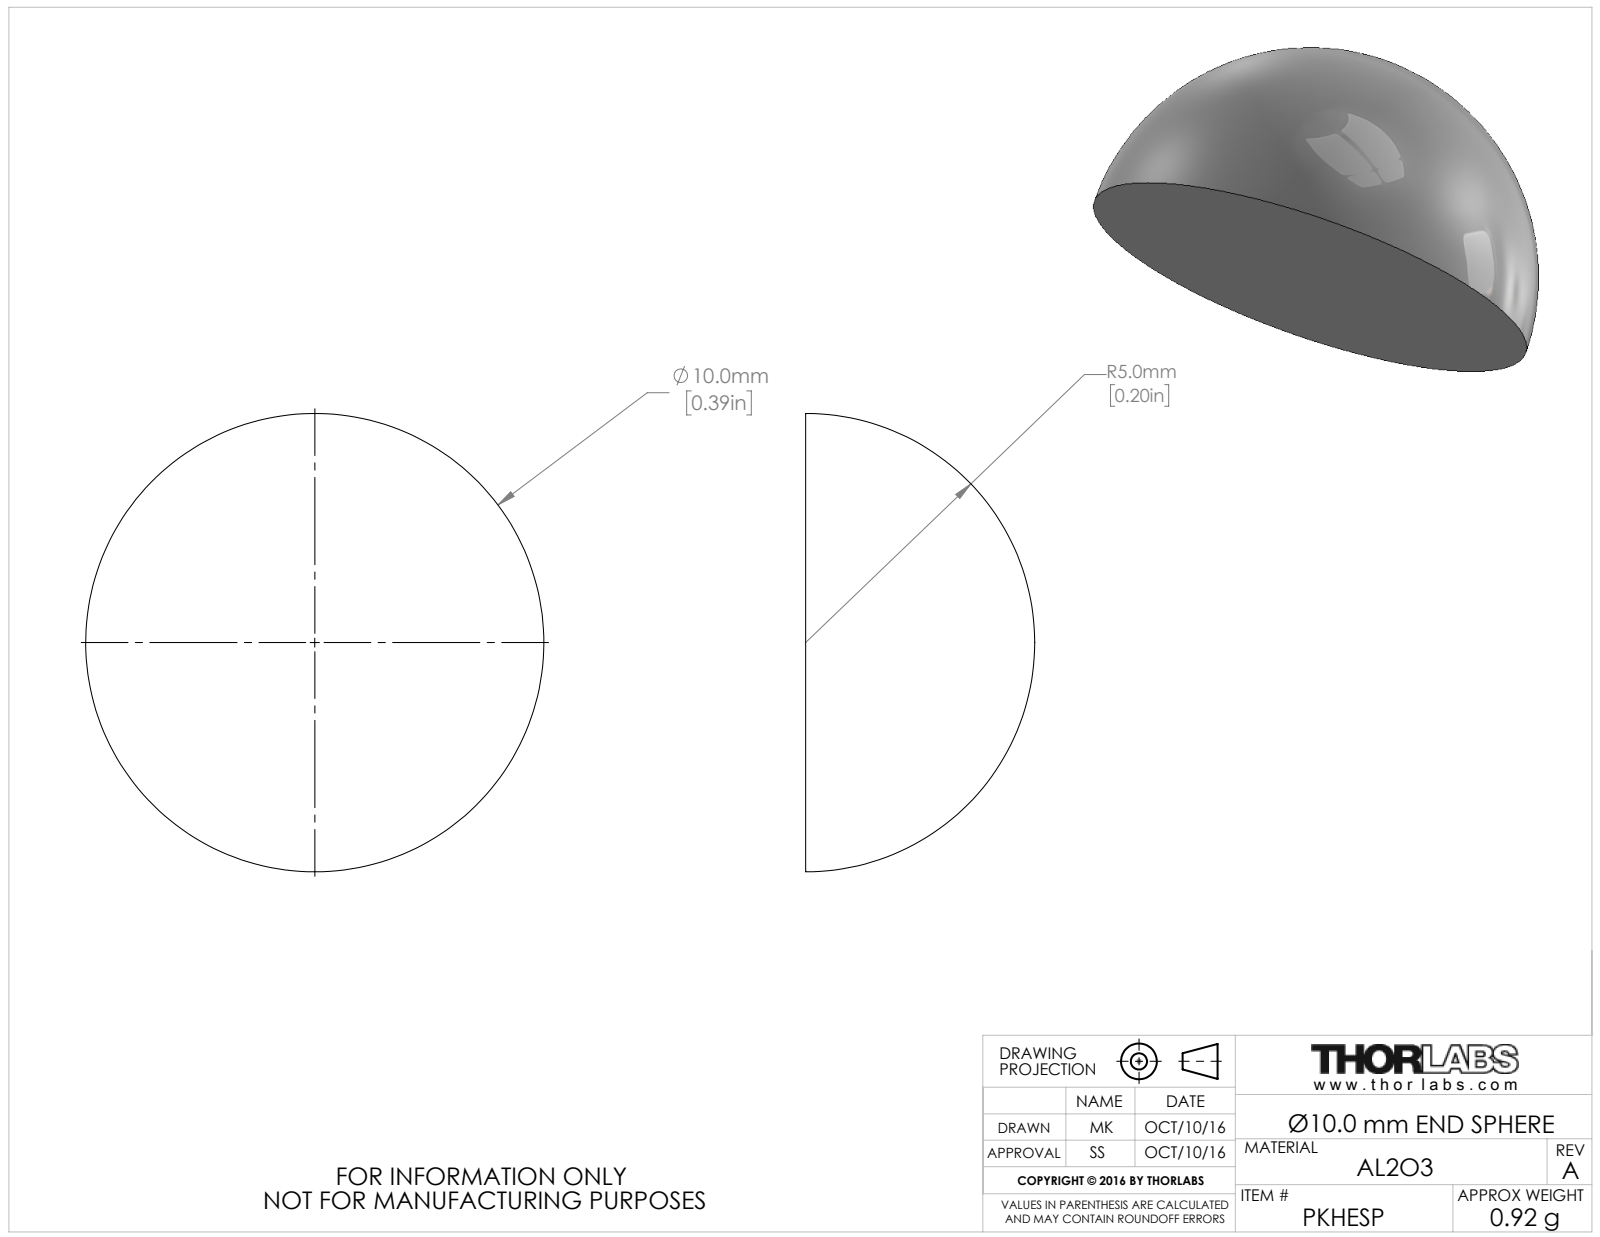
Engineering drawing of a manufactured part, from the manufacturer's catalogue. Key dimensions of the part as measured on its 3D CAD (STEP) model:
Part name (STEP PRODUCT): CTN002732
STEP written by: SolidWorks 2016 (AUTOMOTIVE_DESIGN)
Units: millimetres
Bodies: 1 solid, 3 faces (1 planar, 0 cylindrical, 2 other)
Overall size (bounding box): 10 × 10 × 5
Volume: 262 mm³ · Surface area: 236 mm²
